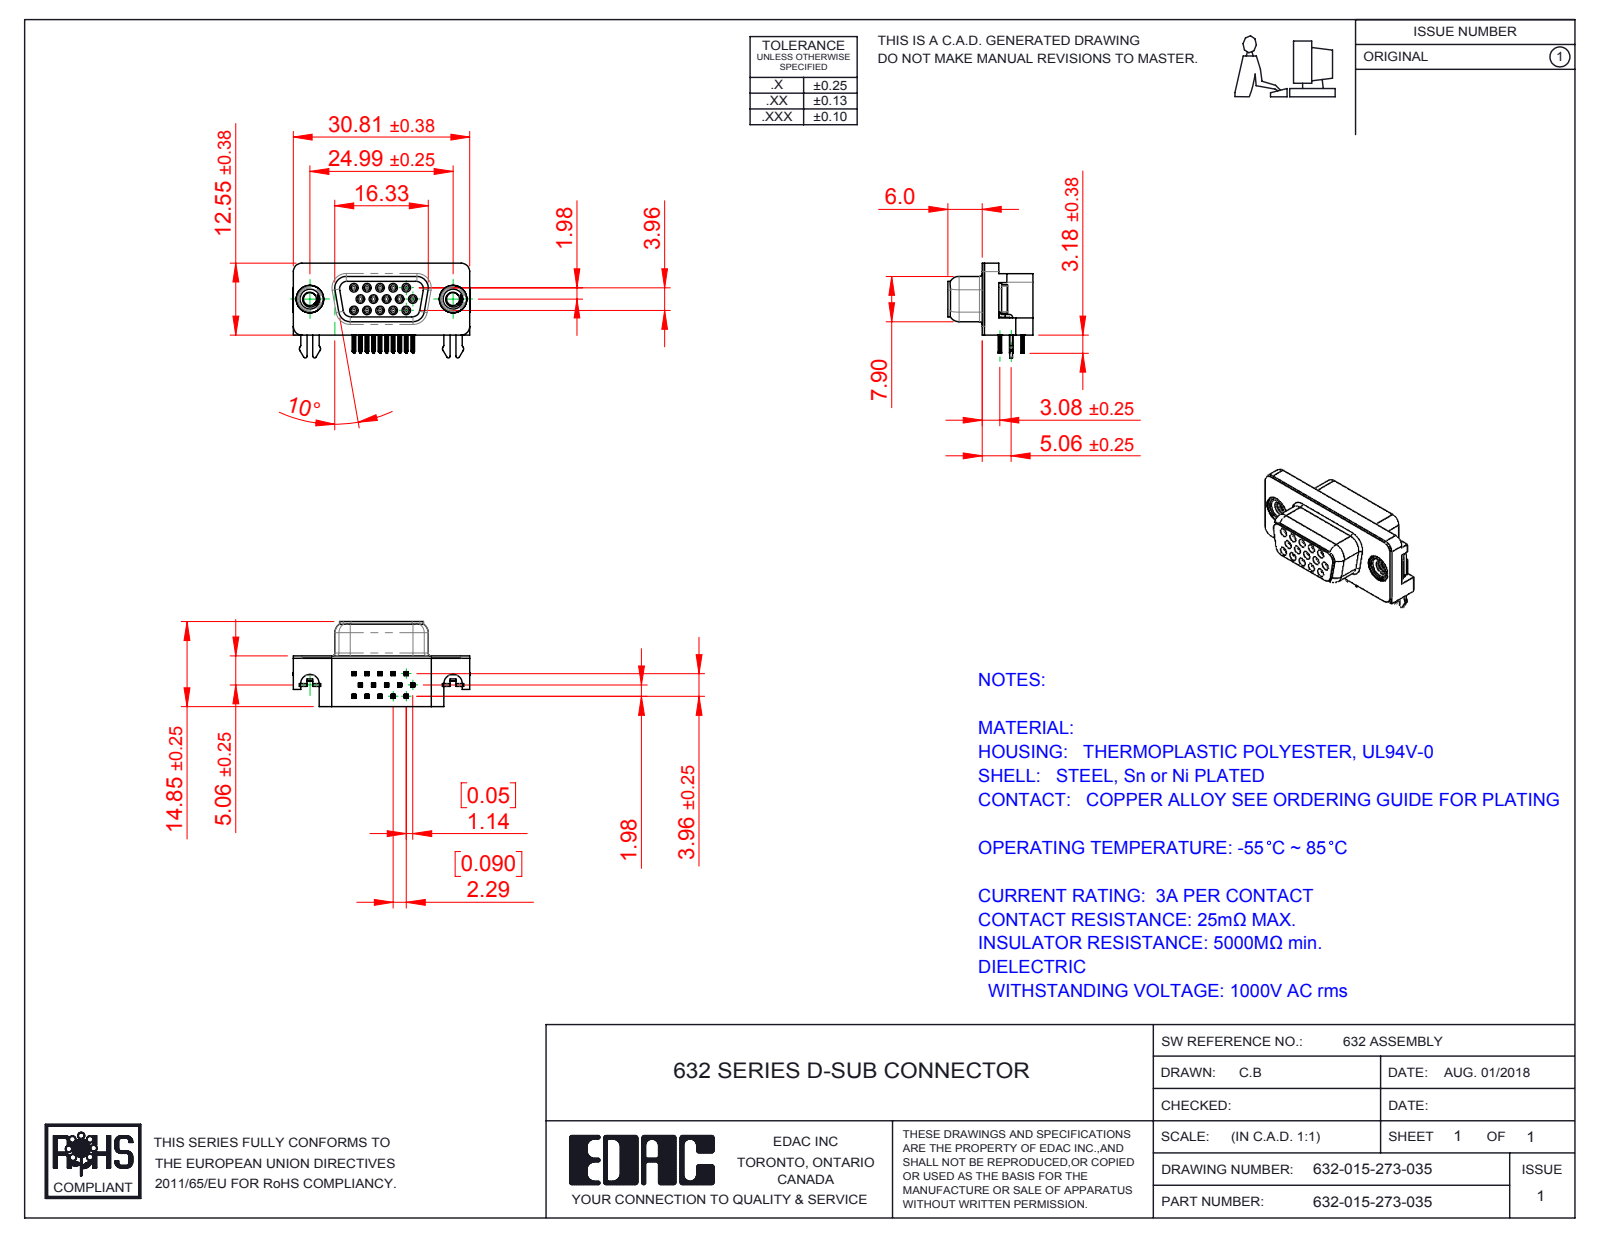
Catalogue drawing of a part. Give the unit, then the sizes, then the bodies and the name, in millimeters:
Units: millimetres
Overall size (bounding box): 30.89 × 16.55 × 14.85
Round holes (diameter × count): ⌀0.8 ×15, ⌀0.9 ×15, ⌀2.26 ×2, ⌀2.5 ×2, ⌀4 ×2, ⌀4.8 ×2, ⌀5 ×2
Round bosses / shafts (diameter × count): ⌀1.2 ×15, ⌀4.9 ×2, ⌀4.75 ×2, ⌀3.9 ×2
Partial cylindrical surfaces — rounded edges, fillets, slot ends (radius × count): R0.1 ×120, R0.15 ×60, R0.35 ×30, R0.34 ×15, R1 ×11, R0.28 ×10, R0.5 ×10, R0.25 ×8
Main face-to-face distances: 0.4, 8.45, 8.85, 1.98, 2.9, 5.95, 2.5, 6.4, 6.7, 7.05
Hole centre spacings: 2.28, 2.29, 3.96, 4.57, 6.05, 3.97, 4.58, 6.86
Volume: 2 996 mm³ · Surface area: 5 339 mm²
Bodies: 23 solids, 2426 faces (1006 planar, 654 cylindrical, 766 other)
Part name (STEP PRODUCT): 632 Contact Top; 632 Contact Middle; 632 Contact Bottom; 632 4-40 Threaded Rivet (+6 more)
STEP written by: SolidWorks 2016 (CONFIG_CONTROL_DESIGN)
